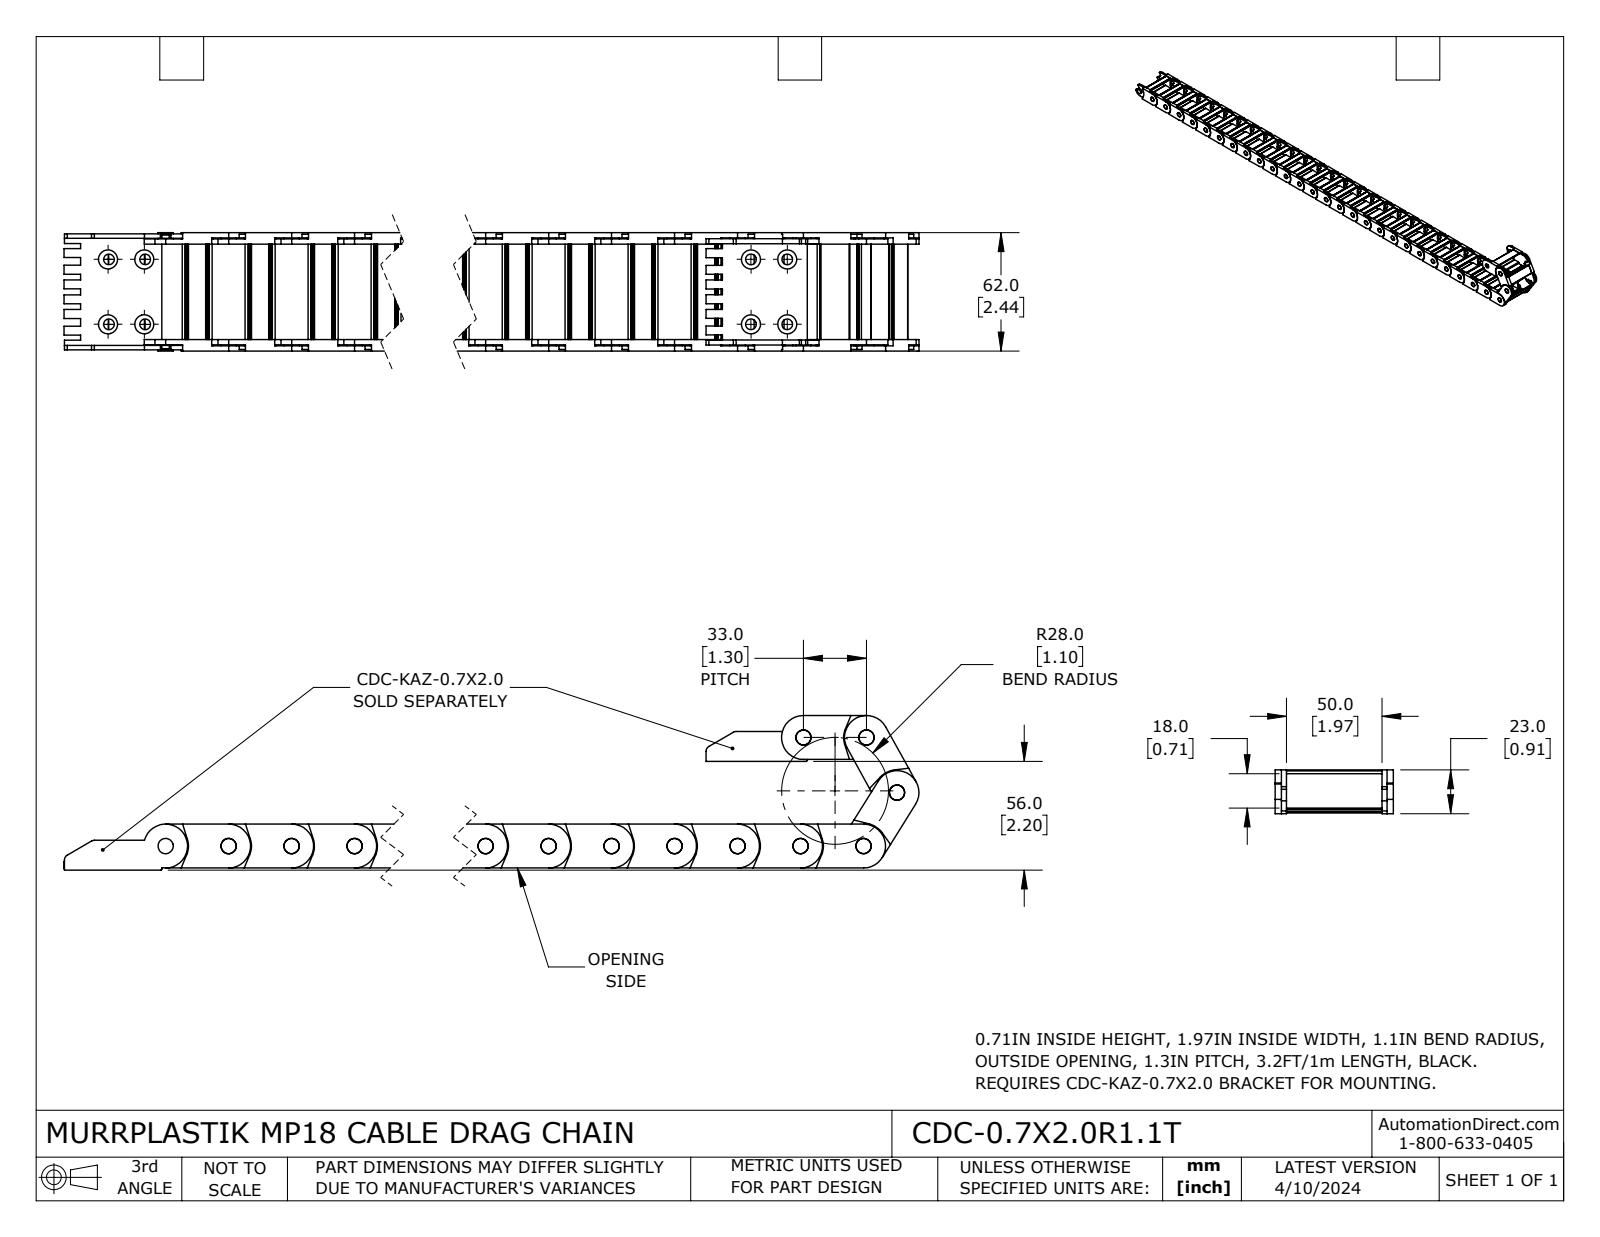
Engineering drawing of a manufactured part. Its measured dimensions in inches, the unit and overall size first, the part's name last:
Units: inches
Overall size (bounding box): 36.661 × 3.143 × 2.441
Round holes (diameter × count): ⌀0.315 ×30
Round bosses / shafts (diameter × count): ⌀0.315 ×1
Partial cylindrical surfaces — rounded edges, fillets, slot ends (radius × count): R0.02 ×120, R0.059 ×120, R0.008 ×60, R0.012 ×60, R0.453 ×31, R0.47 ×31, R0.197 ×30, R0.215 ×30
Main face-to-face distances: 2.205, 0.106, 0.13, 0.236, 2.441, 2.311, 2.075, 2.335, 0.024, 2.098
Hole centre spacings: 1.299, 2.598, 3.898, 5.197, 6.496, 7.795, 9.094, 10.394
Volume: 18.99 in³ · Surface area: 406.4 in²
Bodies: 30 solids, 2280 faces (1110 planar, 1170 cylindrical, 0 other)
Part name (STEP PRODUCT): CDC-0.7X2.0R1.1T
STEP written by: SolidWorks 2023 (CONFIG_CONTROL_DESIGN)
